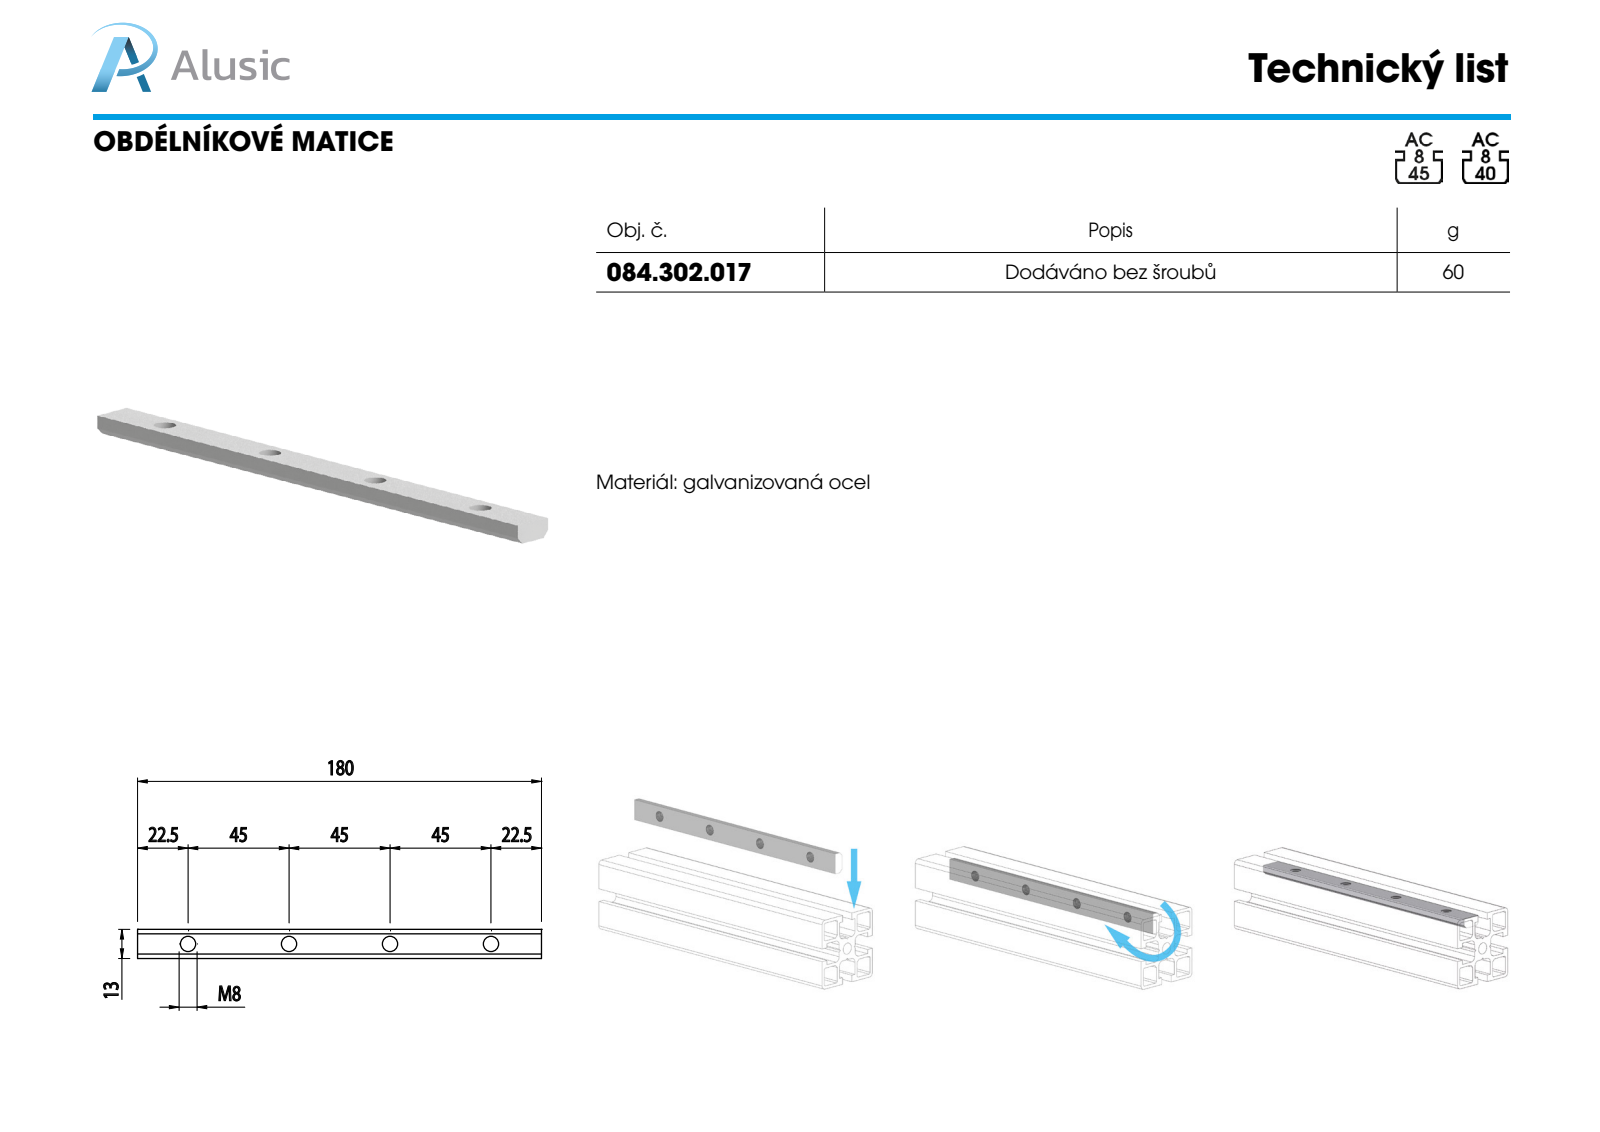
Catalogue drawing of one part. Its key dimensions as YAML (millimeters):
part_name: "084.302.017"
step_written_by: "SolidWorks 2011 (CONFIG_CONTROL_DESIGN)"
units: millimeters
bodies: {solids: 1, faces: 16, planar: 8, cylindrical: 8, other: 0}
overall_size: [180, 13, 6]
volume: 12448
surface_area: 6788
round_holes:
  - {diameter: 6.8, count: 4}
face_to_face_distances: [6, 13, 180]
hole_center_spacings: [45, 90, 135]
